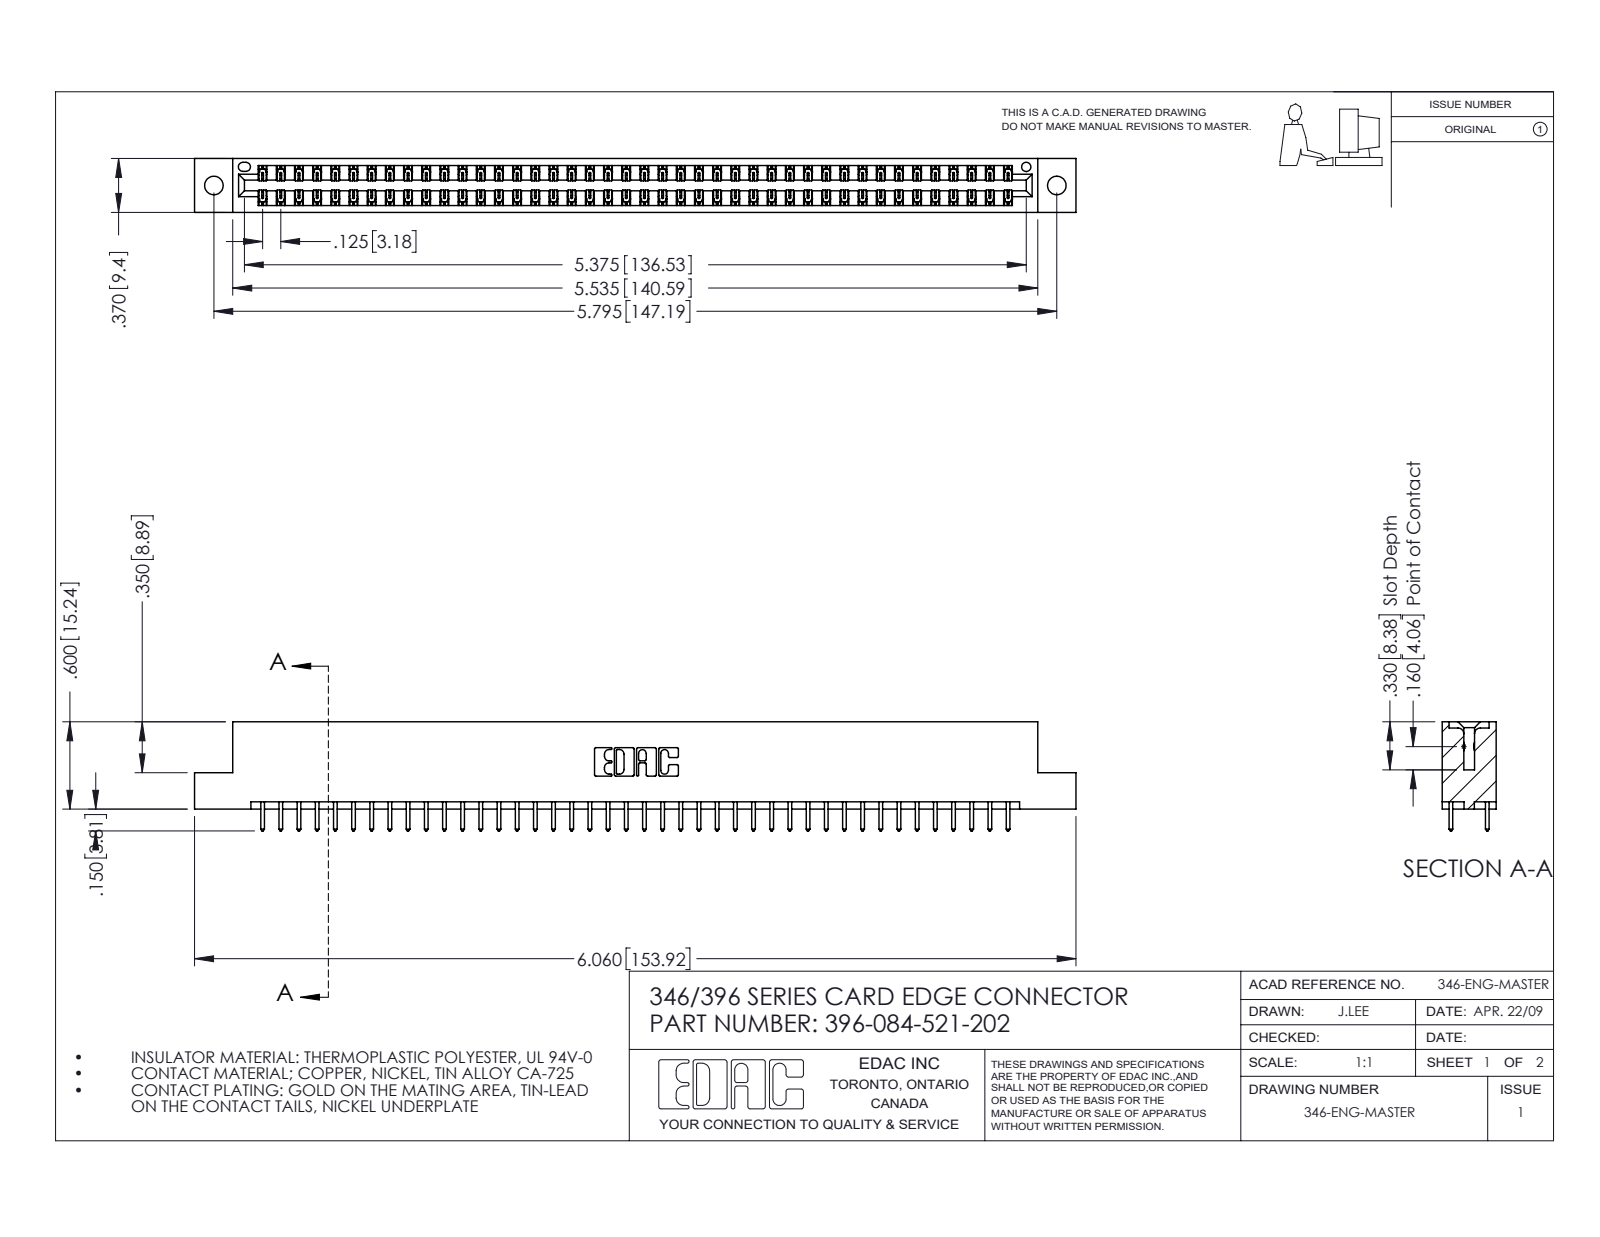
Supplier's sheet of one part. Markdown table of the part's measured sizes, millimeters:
| quantity | value |
| --- | --- |
| part name | 345-292-001_345-293-121; 346 Part_Flush Mounting Lugs - 0.128 Dia; 396-084-521-202 |
| STEP written by | SolidWorks 2016 (CONFIG_CONTROL_DESIGN) |
| units | millimeters |
| bodies | 85 solids, 4490 faces (3016 planar, 1474 cylindrical, 0 other) |
| overall size | 153.9 × 19.1 × 9.4 |
| volume | 14 900 mm³ |
| surface area | 20 030 mm² |
| round holes (diameter × count) | 3.3 × 2, 1.6 × 1 |
| partial cylindrical surfaces (radius × count) | 0.2 × 126, 0.3 × 84, 0.3 × 22, 0.2 × 6, 0.8 × 6, 0.7 × 3, 0.4 × 2, 0.6 × 2 |
| main face-to-face distances | 1.2, 8.2, 6.4, 9.4, 1.8, 7.6, 0.6, 7, 3.8, 5.6 |
| hole center spacings | 6.2, 141.9, 147.2 |
